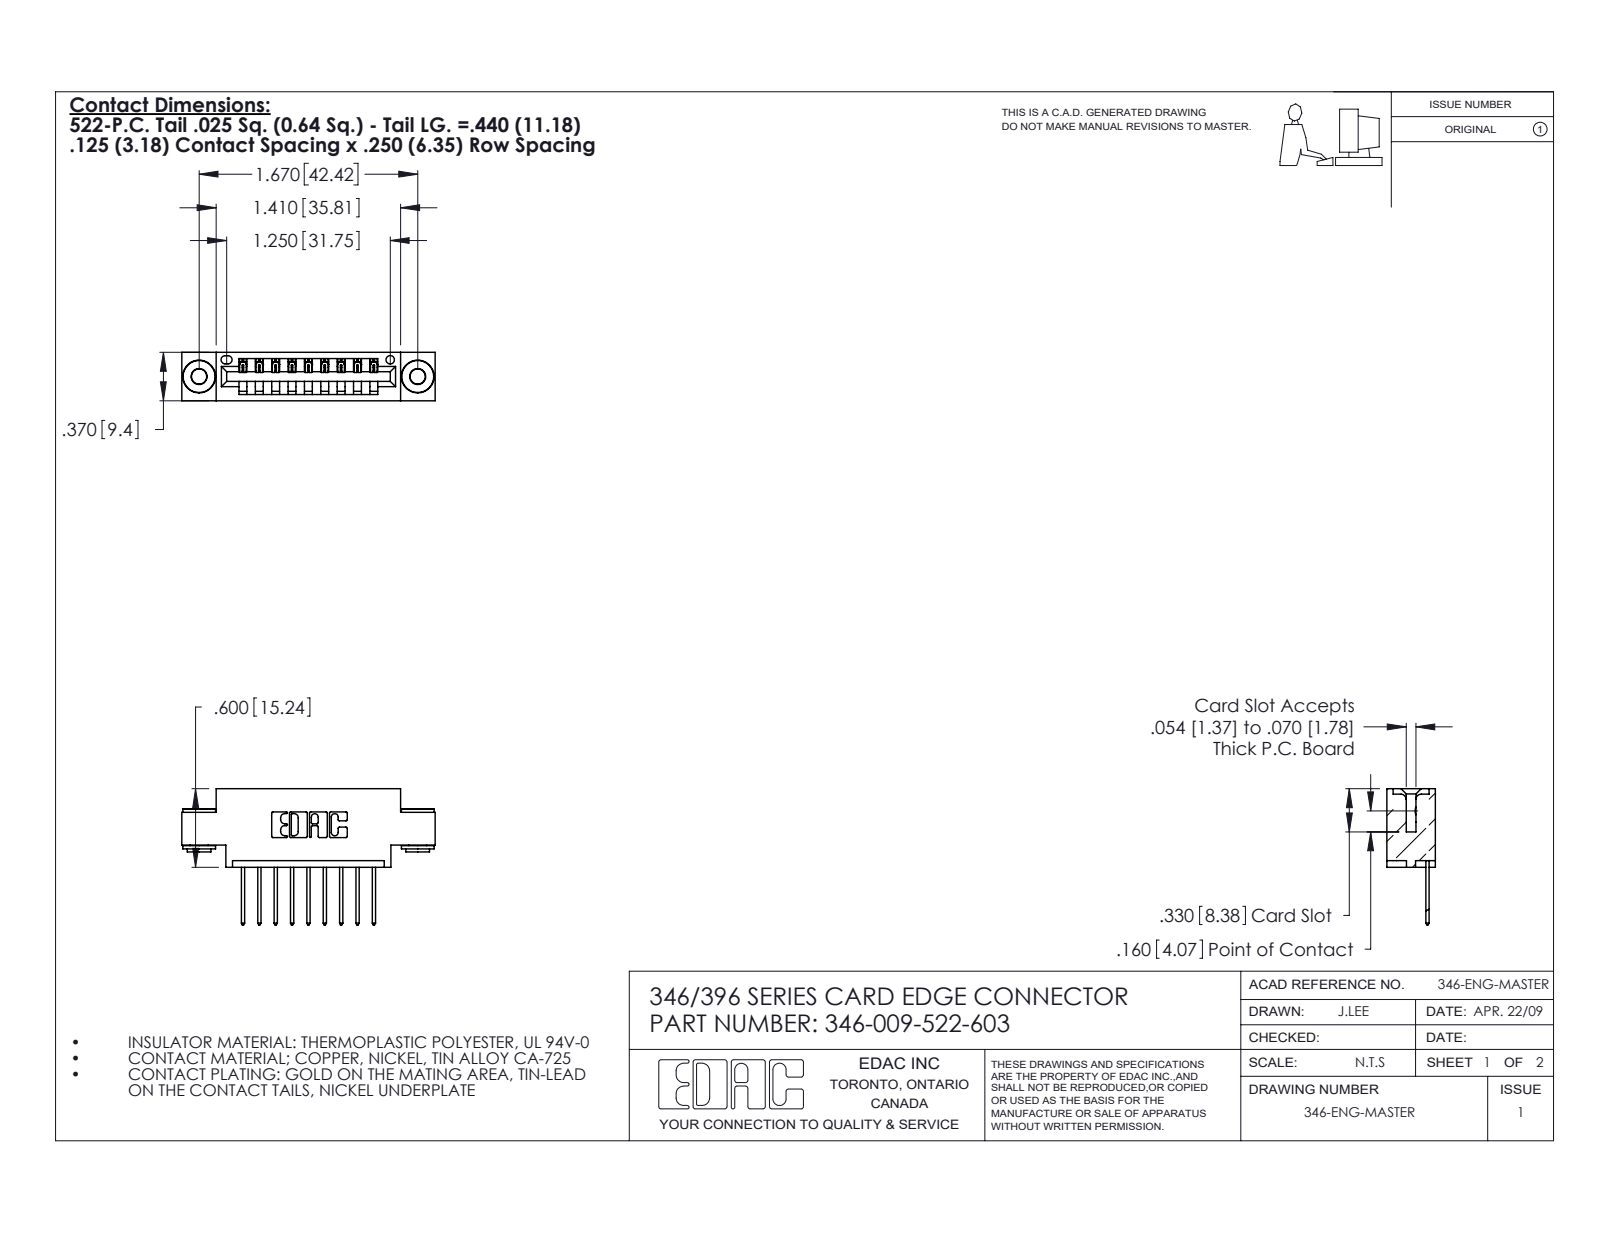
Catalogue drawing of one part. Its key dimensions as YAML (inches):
part_name: "346-009-522-603; 346 Part_0.170 Offset - 0.156 Dia-TH; 345-292-001_345-293-122; 345-250-002_345-250-002-102"
step_written_by: "SolidWorks 2020 (CONFIG_CONTROL_DESIGN)"
units: inches
bodies: {solids: 12, faces: 700, planar: 464, cylindrical: 228, other: 8}
overall_size: [1.935, 1.04, 0.37]
volume: 0.264
surface_area: 8.517
round_holes:
  - {diameter: 0.116, count: 2}
  - {diameter: 0.156, count: 2}
  - {diameter: 0.064, count: 1}
round_bosses_or_shafts:
  - {diameter: 0.25, count: 2}
  - {diameter: 0.18, count: 2}
  - {diameter: 0.136, count: 2}
partial_cylinders:
  - {radius: 0.01, count: 22}
  - {radius: 0.006, count: 18}
  - {radius: 0.01, count: 18}
  - {radius: 0.007, count: 6}
  - {radius: 0.031, count: 6}
  - {radius: 0.026, count: 3}
  - {radius: 0.031, count: 2}
  - {radius: 0.04, count: 2}
face_to_face_distances: [0.25, 0.37, 0.048, 0.322, 0.025, 0.072, 0.298, 0.222, 0.148, 0.1]
hole_center_spacings: [0.246, 1.465, 1.67]
